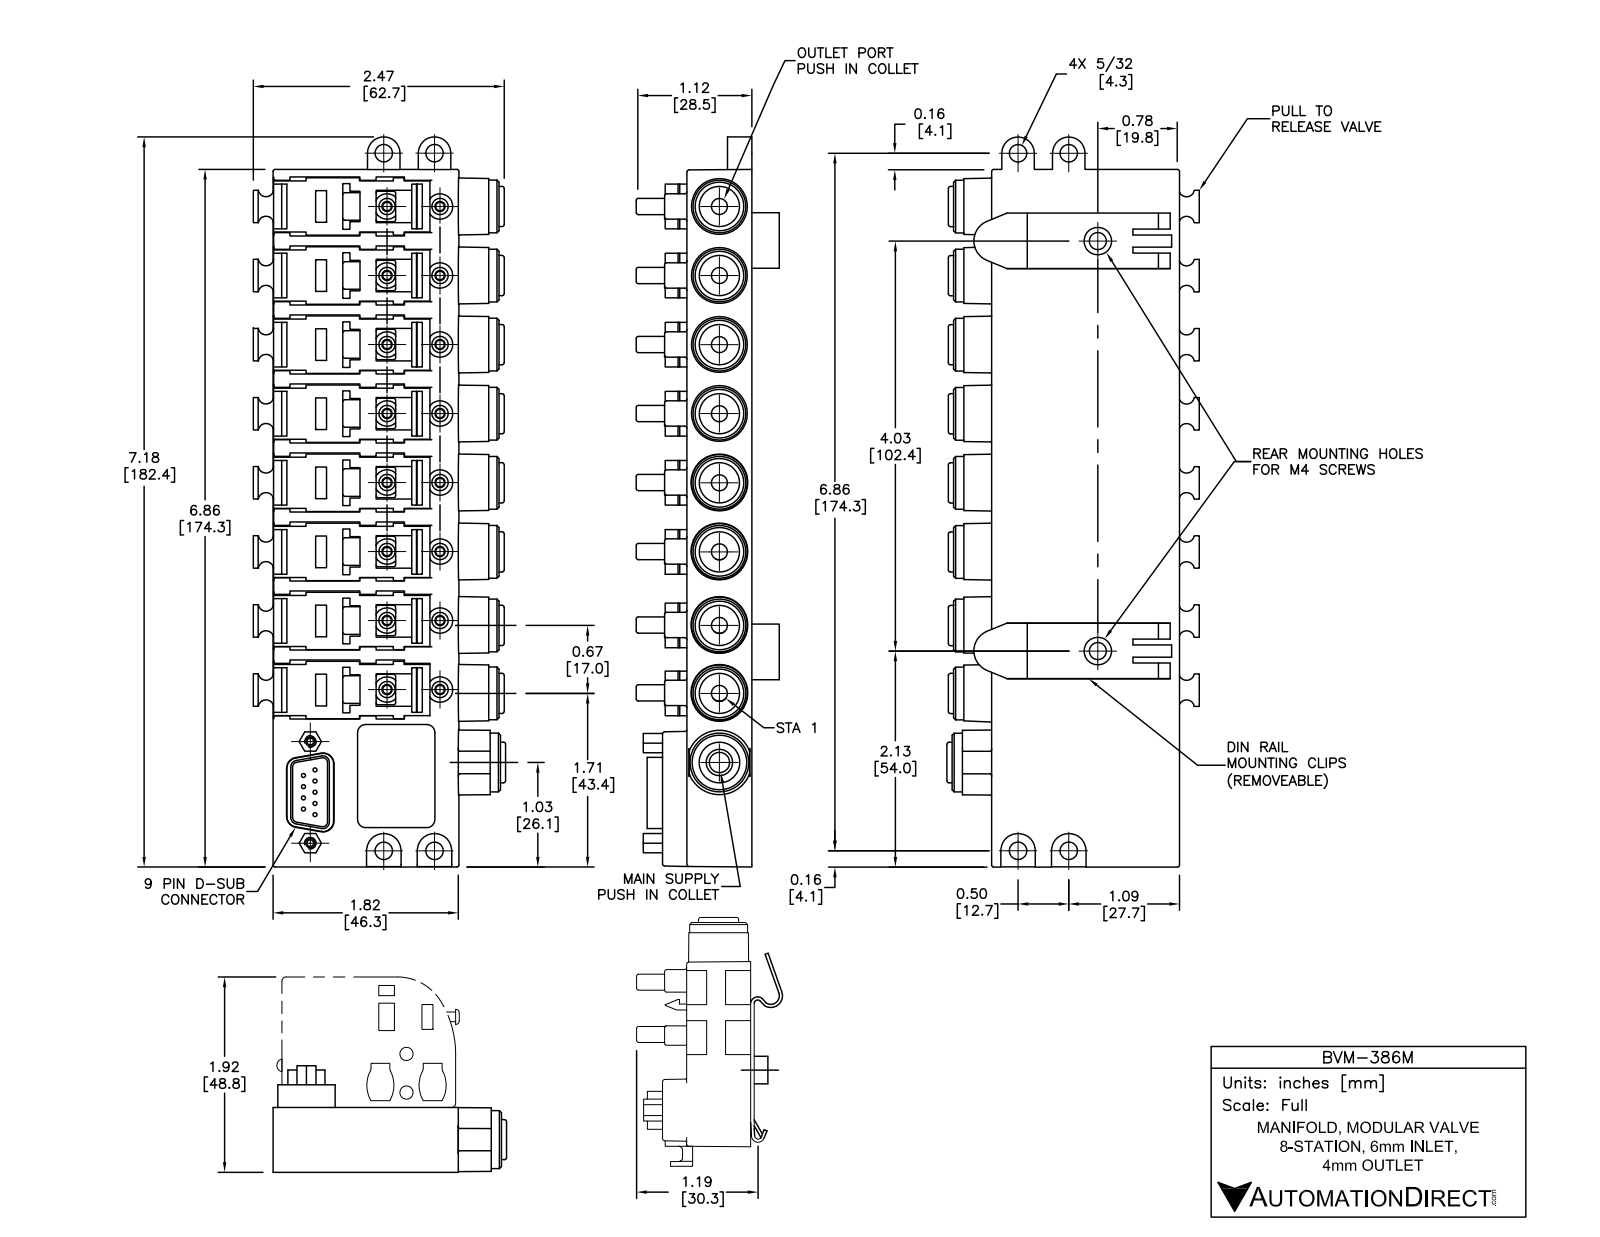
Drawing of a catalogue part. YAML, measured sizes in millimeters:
part_name: "BVM-386M"
step_written_by: "SolidWorks 2013 (AUTOMOTIVE_DESIGN)"
units: millimeters
bodies: {solids: 1, faces: 2031, planar: 1060, cylindrical: 569, other: 402}
overall_size: [182.54, 62.17, 28.5]
volume: 143769
surface_area: 46782
round_holes:
  - {diameter: 3.94, count: 8}
  - {diameter: 4.29, count: 4}
  - {diameter: 2.26, count: 2}
  - {diameter: 5, count: 1}
  - {diameter: 6.5, count: 1}
round_bosses_or_shafts:
  - {diameter: 4, count: 16}
  - {diameter: 1, count: 9}
  - {diameter: 13, count: 8}
  - {diameter: 9.91, count: 8}
  - {diameter: 14.48, count: 1}
  - {diameter: 10.01, count: 1}
partial_cylinders:
  - {radius: 0.5, count: 154}
  - {radius: 0.25, count: 19}
  - {radius: 0.15, count: 16}
  - {radius: 1.9, count: 16}
  - {radius: 3.12, count: 16}
  - {radius: 2.4, count: 8}
  - {radius: 3.4, count: 8}
  - {radius: 1.14, count: 4}
face_to_face_distances: [16, 14.4, 1.6, 17, 0.5, 2, 6, 1.5, 5, 1.1]
hole_center_spacings: [17.02, 34.04, 51.05, 68.07, 85.09, 12.5, 34.03, 51.06]
